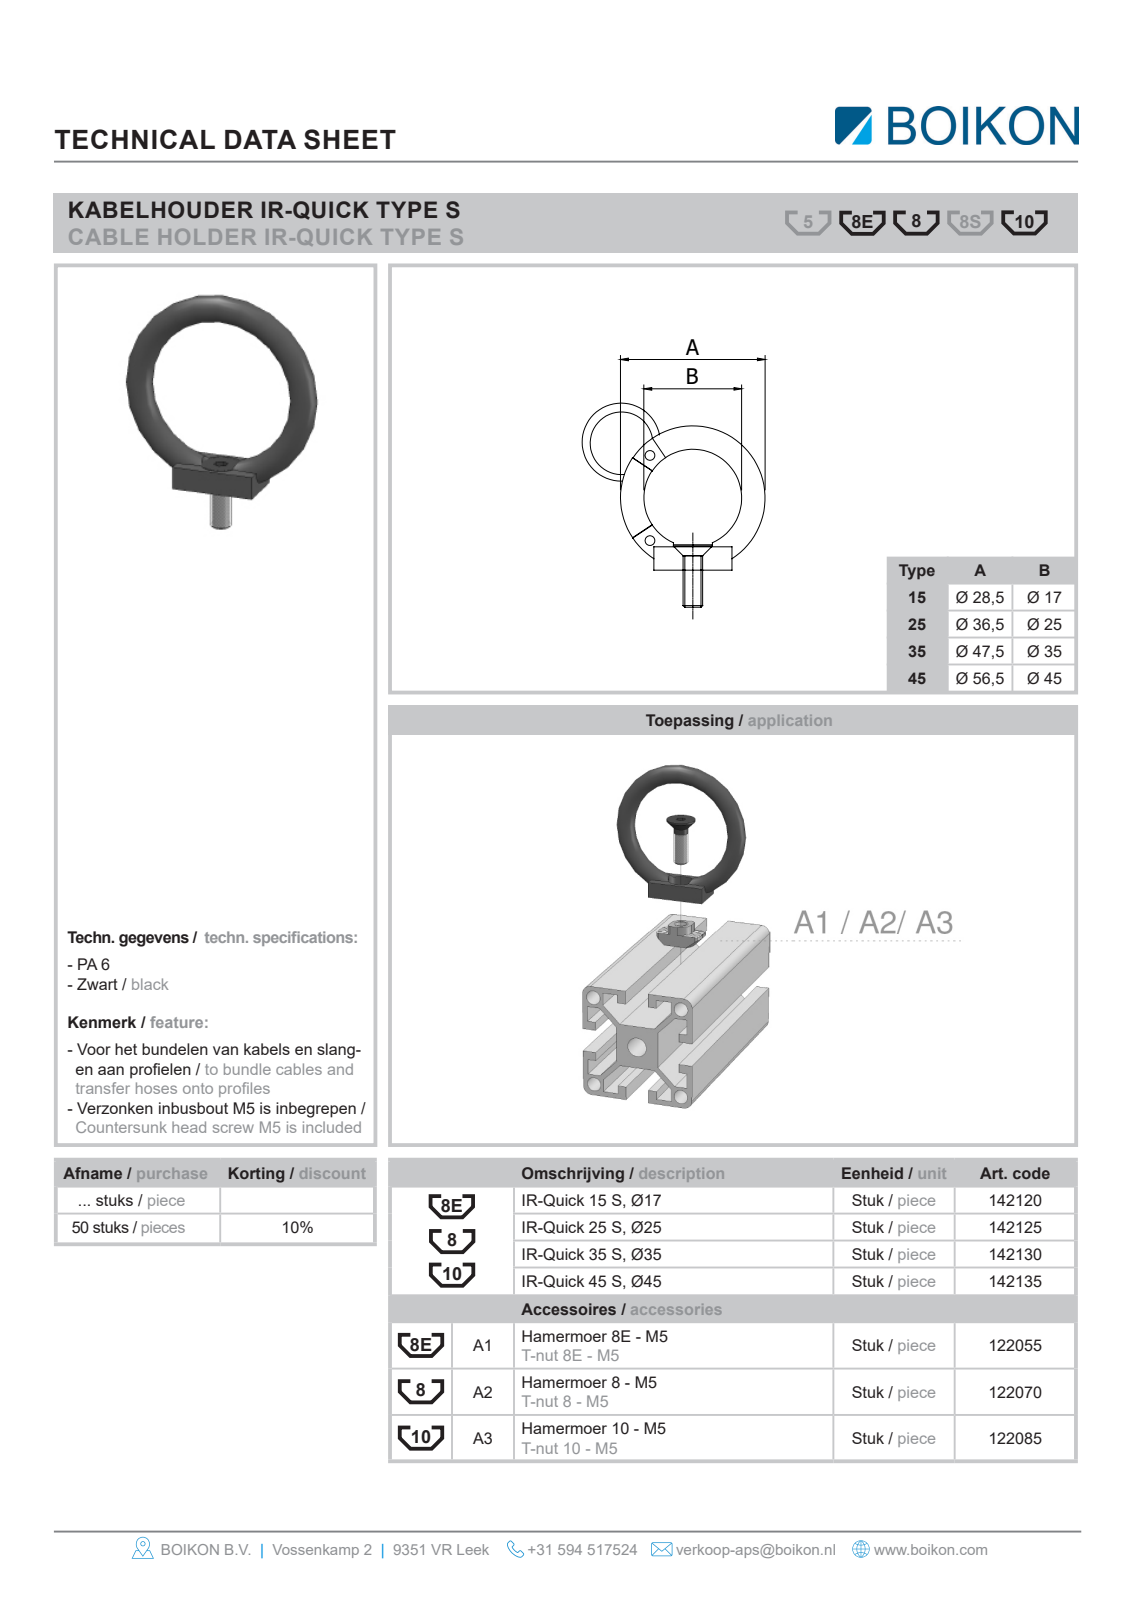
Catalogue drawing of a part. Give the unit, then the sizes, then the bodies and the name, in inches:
Units: inches
Overall size (bounding box): 2.52 × 2.224 × 0.472
Round holes (diameter × count): ⌀0.217 ×1, ⌀0.354 ×1
Round bosses / shafts (diameter × count): ⌀0.335 ×1, ⌀0.197 ×1, ⌀0.158 ×1
Main face-to-face distances: 0.217, 0.472, 0.118, 0.098, 0.787, 0.236, 0.138, 0.02, 0.295, 0.394
Volume: 0.308 in³ · Surface area: 5.833 in²
Bodies: 2 solids, 33 faces (24 planar, 5 cylindrical, 4 other)
Part name (STEP PRODUCT): Root; 142135IR-Quick 45 S, rond 45-8EBOIKON; DIN 7984-M5x10-8.8Cheese-head screw0
STEP written by: HiCAD 2013 1802.4 Build 509 (AUTOMOTIVE_DESIGN)
